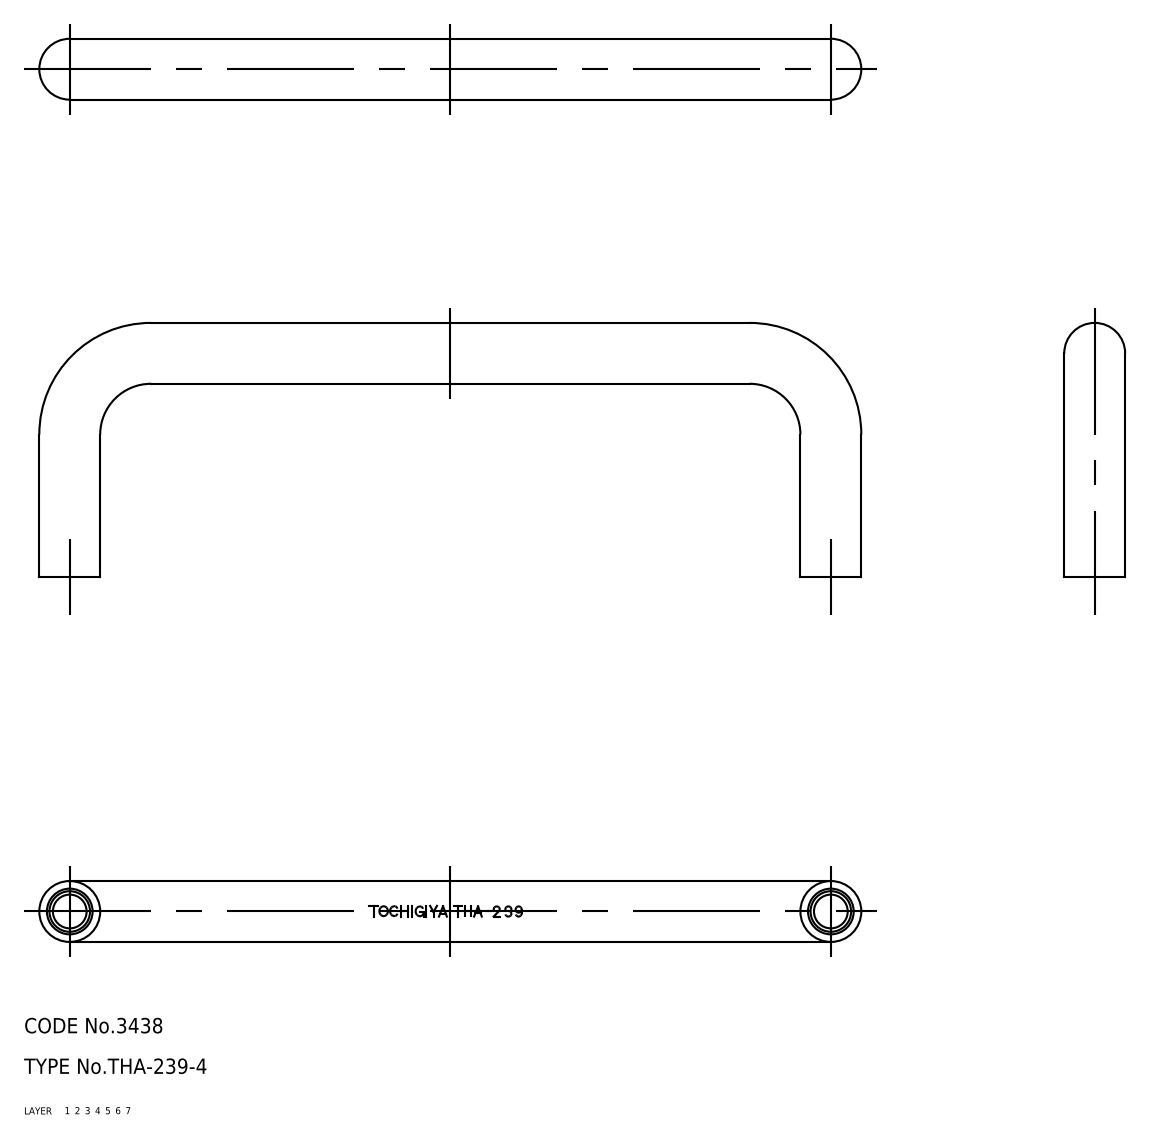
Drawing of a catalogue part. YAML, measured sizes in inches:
part_name: "pull"
step_written_by: "CADfix (AUTOMOTIVE_DESIGN)"
units: inches
bodies: {solids: 1, faces: 18, planar: 0, cylindrical: 0, other: 18}
overall_size: [6.378, 1.969, 0.472]
volume: 1.489
surface_area: 14.24
